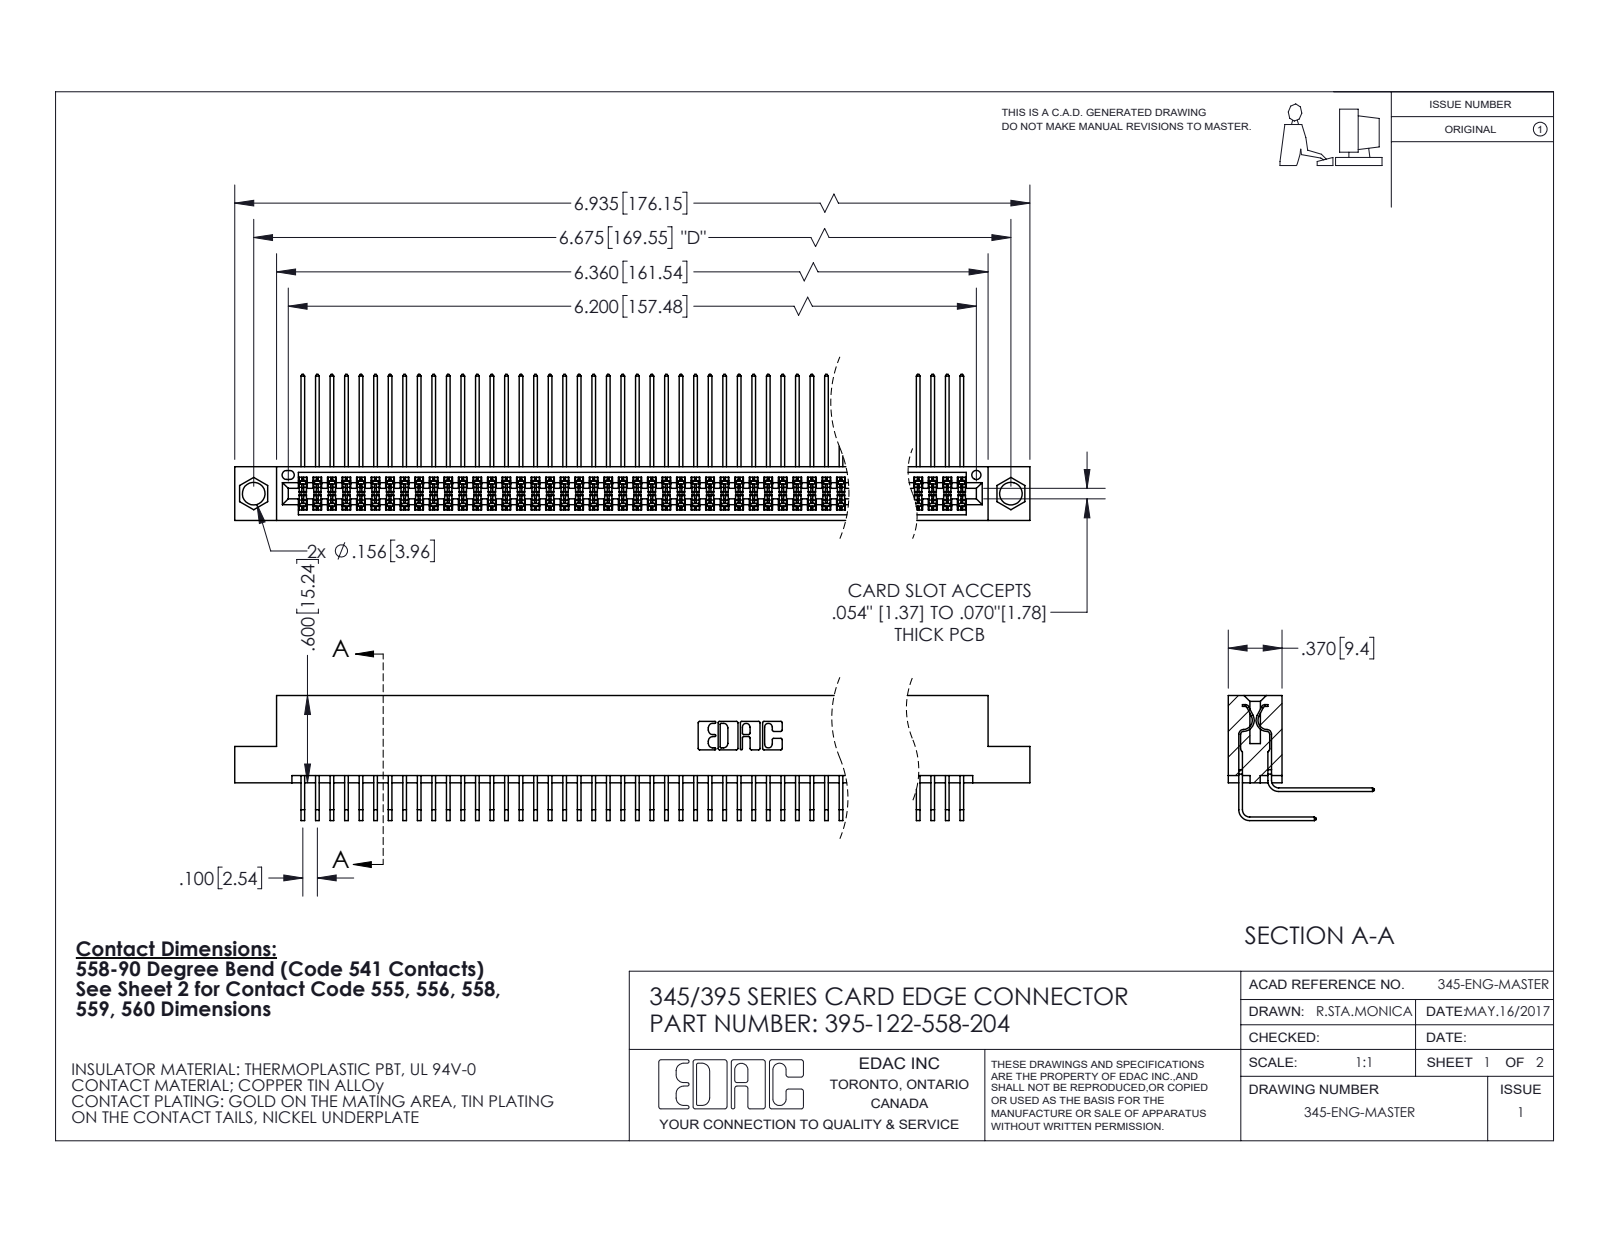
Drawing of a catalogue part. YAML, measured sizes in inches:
part_name: "345-292-001_558 559 Tail - 1; 345 Part_Flush Mounting Lugs - 0.156 Dia-TI; 345-292-001_558 Tail - 2; 395-122-558-204"
step_written_by: "SolidWorks 2020 (CONFIG_CONTROL_DESIGN)"
units: inches
bodies: {solids: 123, faces: 6484, planar: 4364, cylindrical: 2120, other: 0}
overall_size: [6.935, 1.005, 0.859]
volume: 1.091
surface_area: 46.45
round_holes:
  - {diameter: 0.156, count: 2}
  - {diameter: 0.064, count: 1}
partial_cylinders:
  - {radius: 0.006, count: 183}
  - {radius: 0.01, count: 22}
  - {radius: 0.007, count: 6}
  - {radius: 0.031, count: 6}
  - {radius: 0.026, count: 3}
  - {radius: 0.014, count: 2}
  - {radius: 0.019, count: 2}
  - {radius: 0.022, count: 2}
face_to_face_distances: [0.072, 0.298, 0.2, 0.37, 0.098, 0.272, 0.025, 0.225, 0.025, 0.175]
hole_center_spacings: [0.27, 6.439, 6.675]
